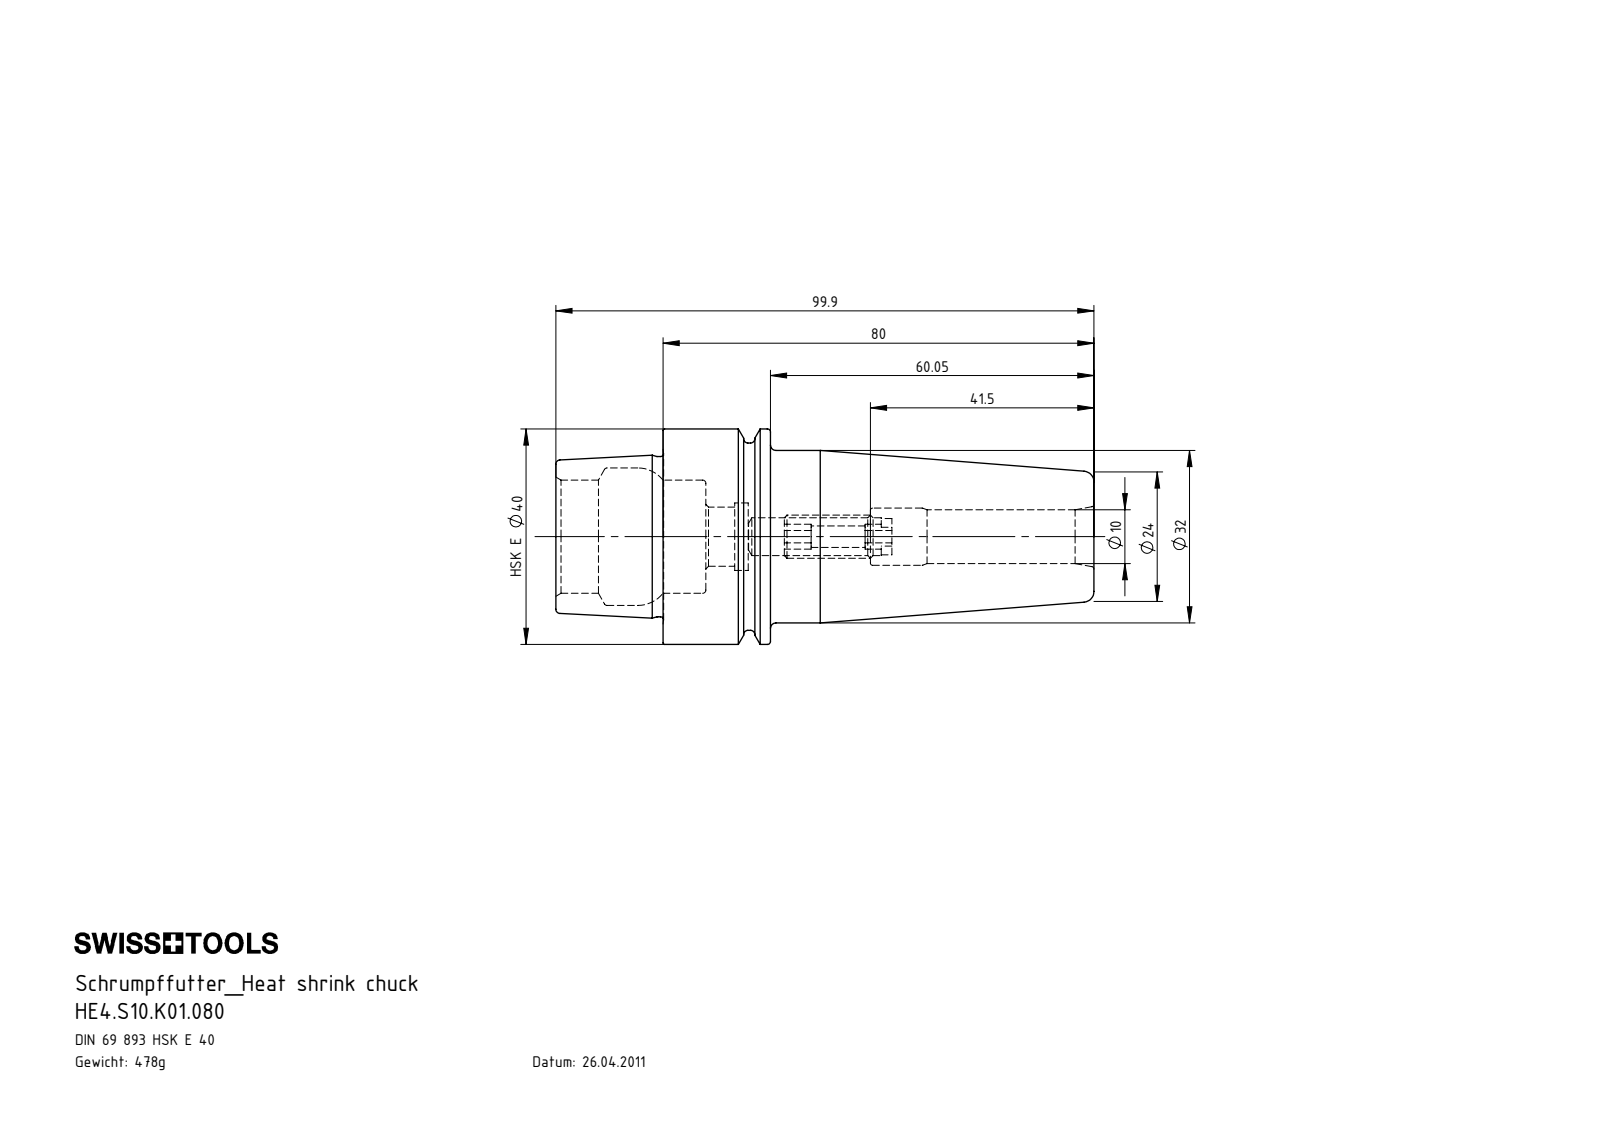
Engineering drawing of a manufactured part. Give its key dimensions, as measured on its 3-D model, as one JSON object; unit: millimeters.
{"part_name": "HE4-S10.K01.080; ERU-AN3.K01.020_A; HE4-S10.K01.080_B_Fertigbearbeitung", "step_written_by": "SolidWorks 2012 (AUTOMOTIVE_DESIGN)", "units": "millimeters", "bodies": {"solids": 2, "faces": 137, "planar": 43, "cylindrical": 34, "other": 60}, "overall_size": [99.9, 40, 40], "volume_mm3": 60927, "surface_area_mm2": 16965, "round_holes": [[4, 1], [5, 1], [7, 1], [10, 1], [10.6, 1], [11, 1], [12.5, 1], [21, 1], [25.5, 1]], "round_bosses_or_shafts": [[40, 1], [34.75, 1], [32, 1], [29.71, 1], [8, 1]], "face_to_face_distances": [19.95, 80, 60.05, 7.95, 12, 72.05, 19.9, 27.85, 39.85, 99.9]}
